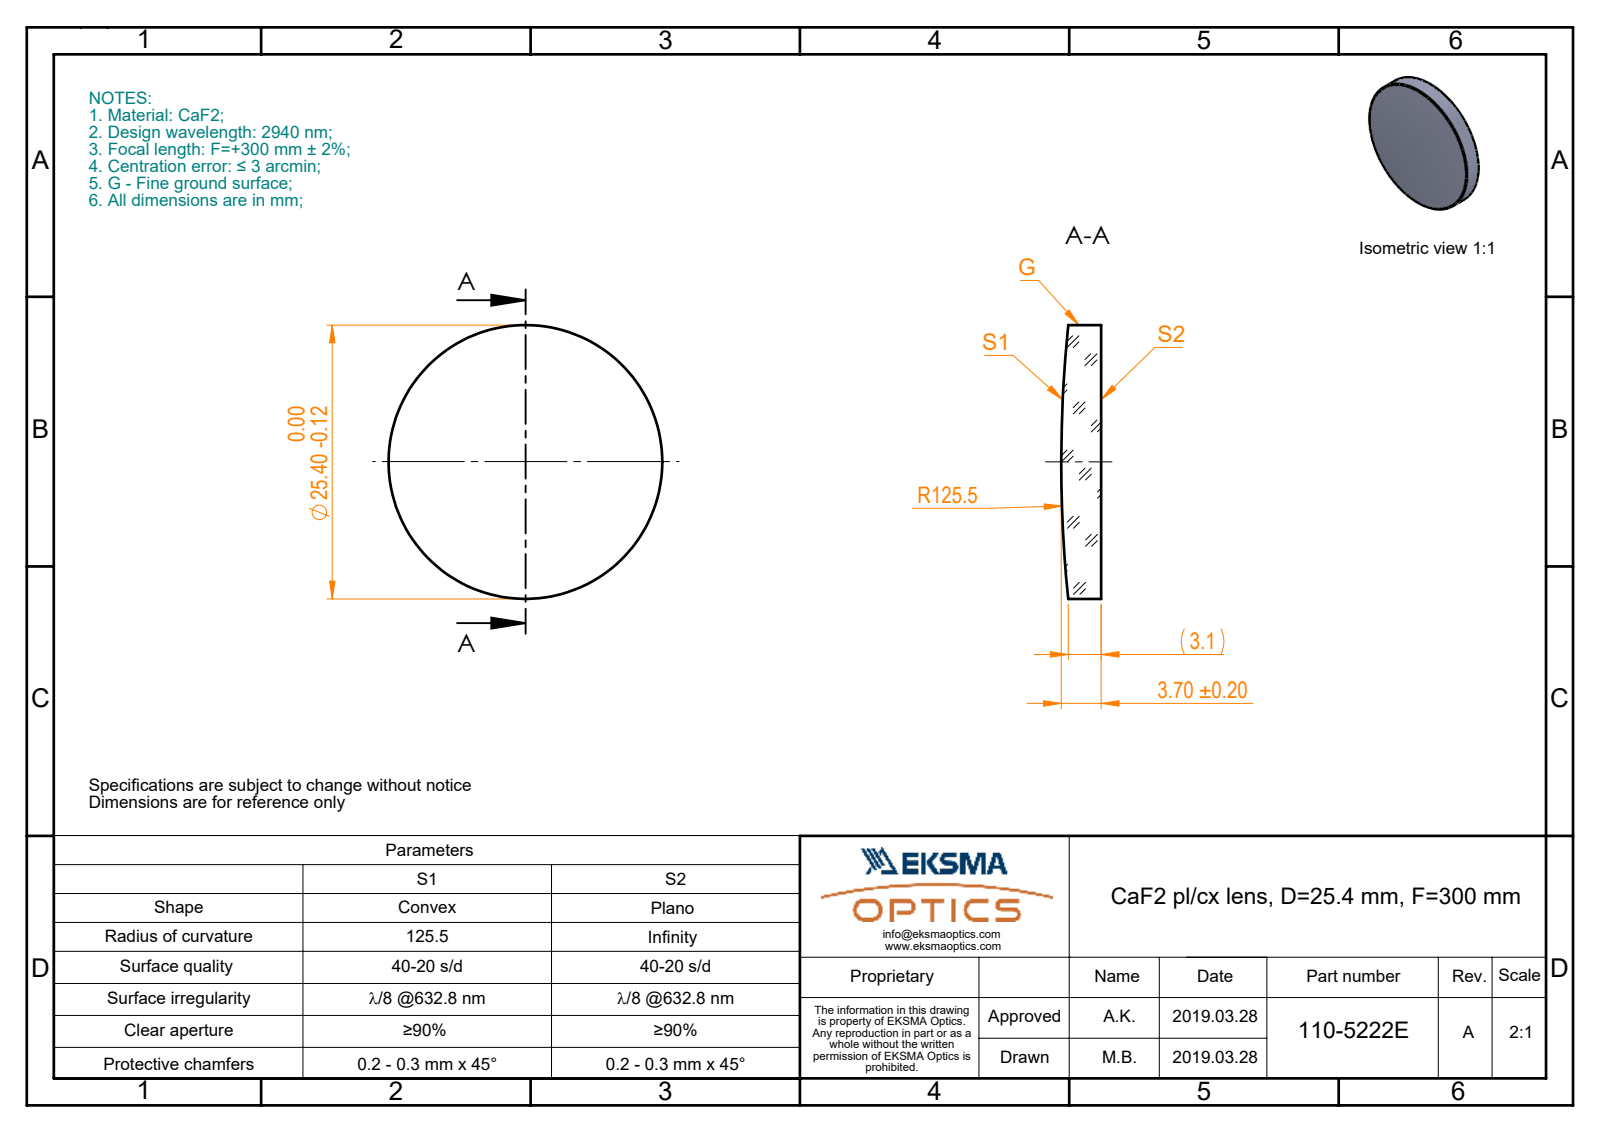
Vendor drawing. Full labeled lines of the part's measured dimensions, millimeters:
Part name (STEP PRODUCT): 110-5222E CaF2 pl-cx 25.4 F300
STEP written by: SolidWorks 2017 (CONFIG_CONTROL_DESIGN)
Units: millimetres
Bodies: 1 solid, 5 faces (1 planar, 2 cylindrical, 2 other)
Overall size (bounding box): 25.4 × 25.4 × 3.7
Volume: 1 712 mm³ · Surface area: 1 259 mm²
Round bosses / shafts (diameter × count): ⌀25.4 ×1
